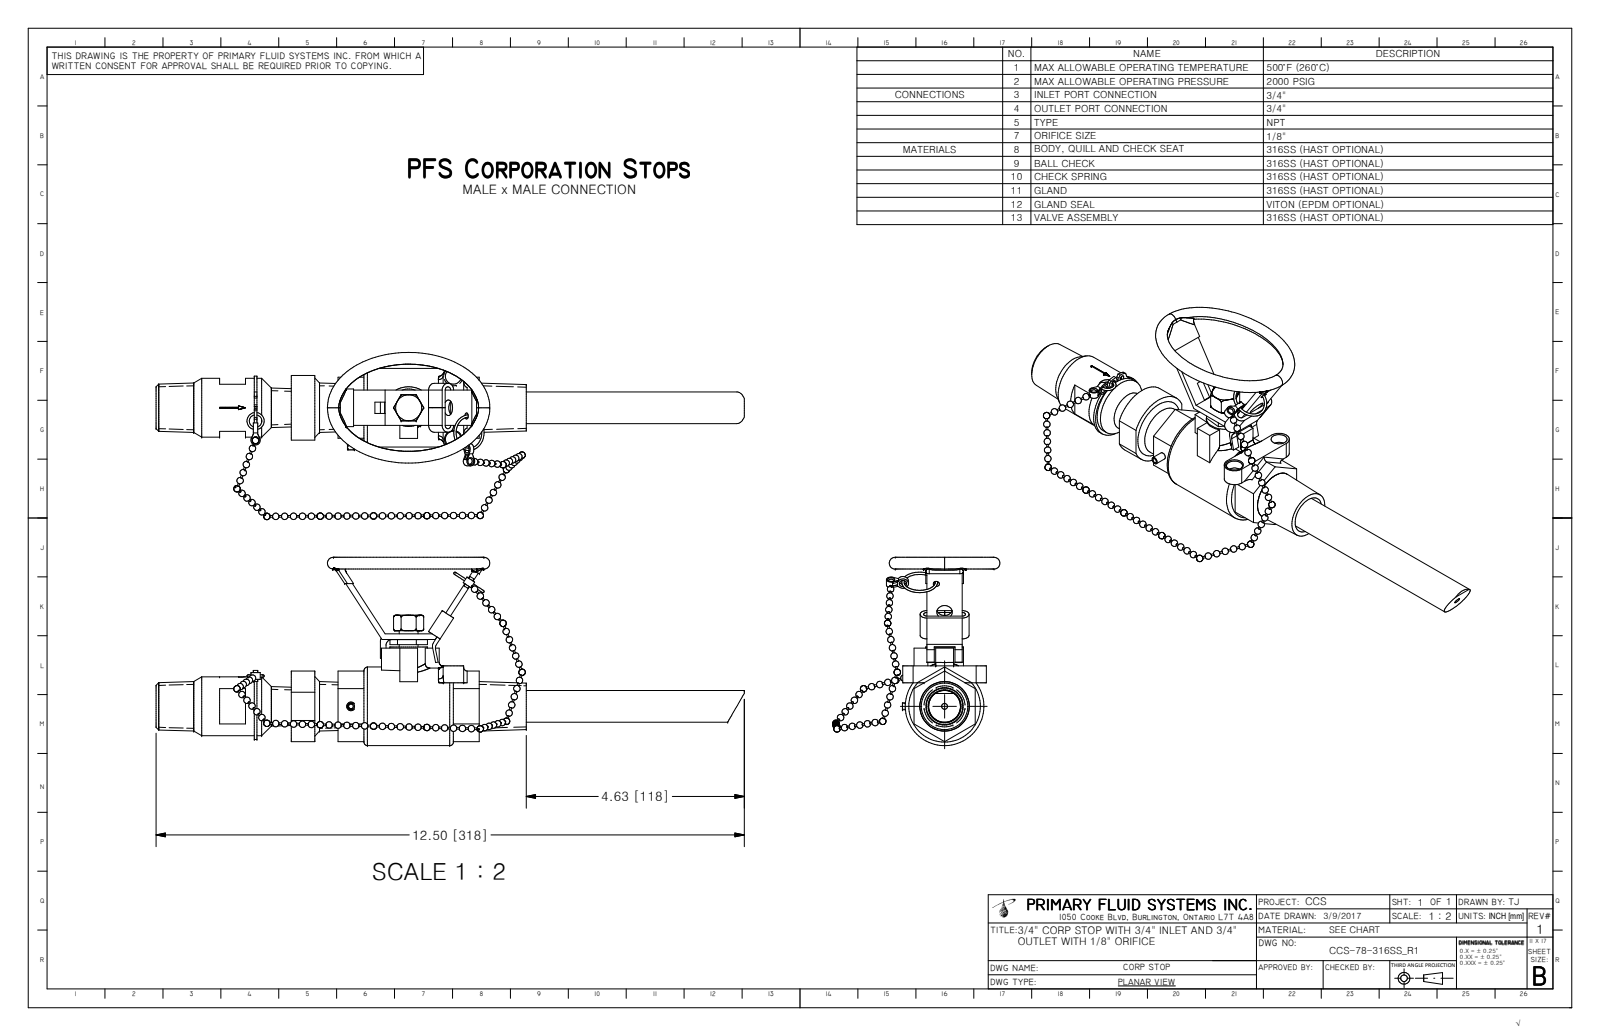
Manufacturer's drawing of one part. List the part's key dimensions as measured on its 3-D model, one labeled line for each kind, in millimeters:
Part name (STEP PRODUCT): CCS-78-316SS_R0
STEP written by: Autodesk Inventor 2009 (AUTOMOTIVE_DESIGN)
Units: millimetres
Bodies: 0 solids, 417 faces (178 planar, 42 cylindrical, 197 other)
Overall size (bounding box): 317.5 × 101.6 × 90.2
Round holes (diameter × count): ⌀2.5 ×1, ⌀3.2 ×1, ⌀6.4 ×1, ⌀11.9 ×1
Round bosses / shafts (diameter × count): ⌀42.4 ×1, ⌀34.1 ×1, ⌀31.8 ×1, ⌀20.3 ×1, ⌀17.1 ×1, ⌀10.2 ×1, ⌀3.8 ×1
Partial cylindrical surfaces — rounded edges, fillets, slot ends (radius × count): R1.9 ×4, R1.3 ×2, R1.4 ×2, R3.7 ×2, R3.8 ×2, R5 ×2, R3.2 ×1, R4.2 ×1
Main face-to-face distances: 33, 3, 25.4, 3.8, 29.2, 14, 7, 26, 3.2, 3
Hole centre spacings: 16.7
